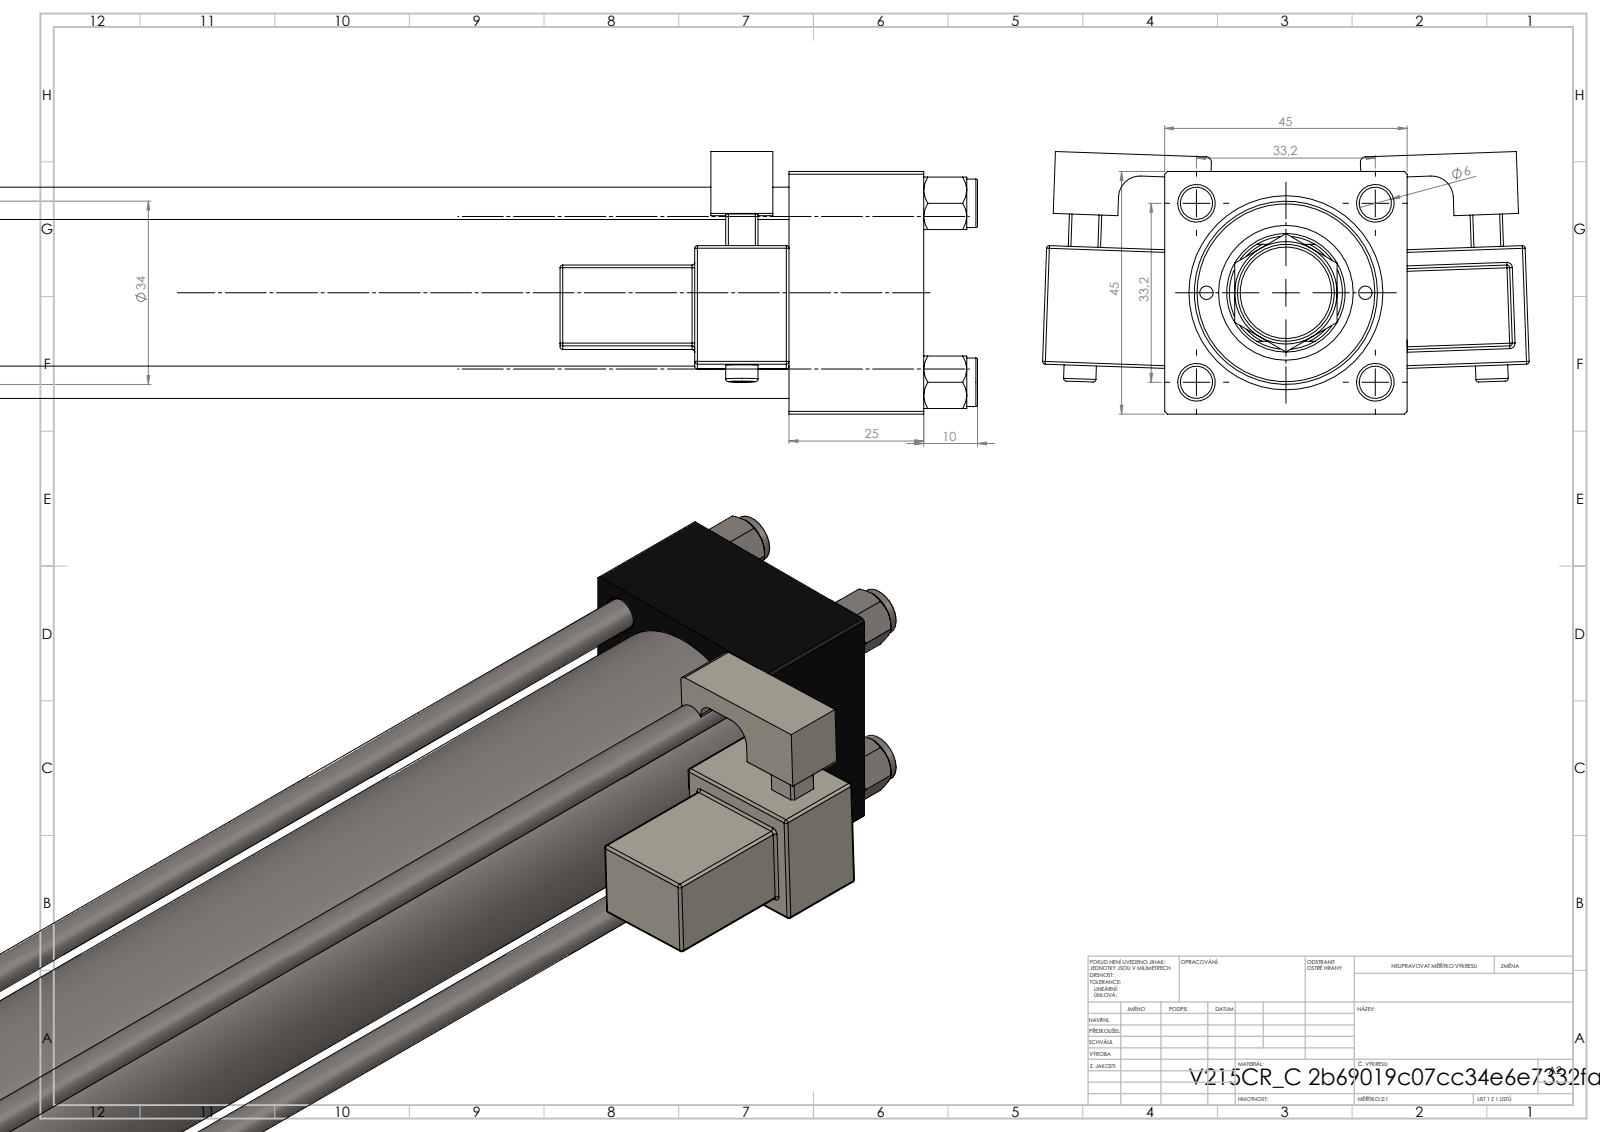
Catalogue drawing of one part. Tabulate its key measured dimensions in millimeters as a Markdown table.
| quantity | value |
| --- | --- |
| part name | V215CR_C_TYCINKA; V215CR_VCP_C; V215_VC_A; MFA (+3 more) |
| STEP written by | SolidWorks 2019 (CONFIG_CONTROL_DESIGN) |
| units | millimeters |
| bodies | 14 solids, 1363 faces (605 planar, 154 cylindrical, 604 other) |
| overall size | 421 × 90.31 × 48.72 |
| volume | 447 731 mm³ |
| surface area | 170 085 mm² |
| round holes (diameter × count) | 6 × 4, 2.5 × 2, 7 × 2, 13.16 × 2, 20 × 2, 10.5 × 1, 22 × 1, 24 × 1, 25 × 1, 32 × 1, 33 × 1 |
| round bosses / shafts (diameter × count) | 9 × 4, 6 × 2, 38 × 1, 34 × 1, 18 × 1, 11 × 1 |
| partial cylindrical surfaces (radius × count) | 0.5 × 48, 1 × 2, 2.5 × 2, 4 × 2, 10.5 × 1 |
| main face-to-face distances | 45, 25, 3, 305, 280, 353, 22.99, 262.5, 328, 13 |
| hole center spacings | 16.7, 23.48, 33.2, 35.47, 14.75, 46.95, 29.5, 305.5 |
